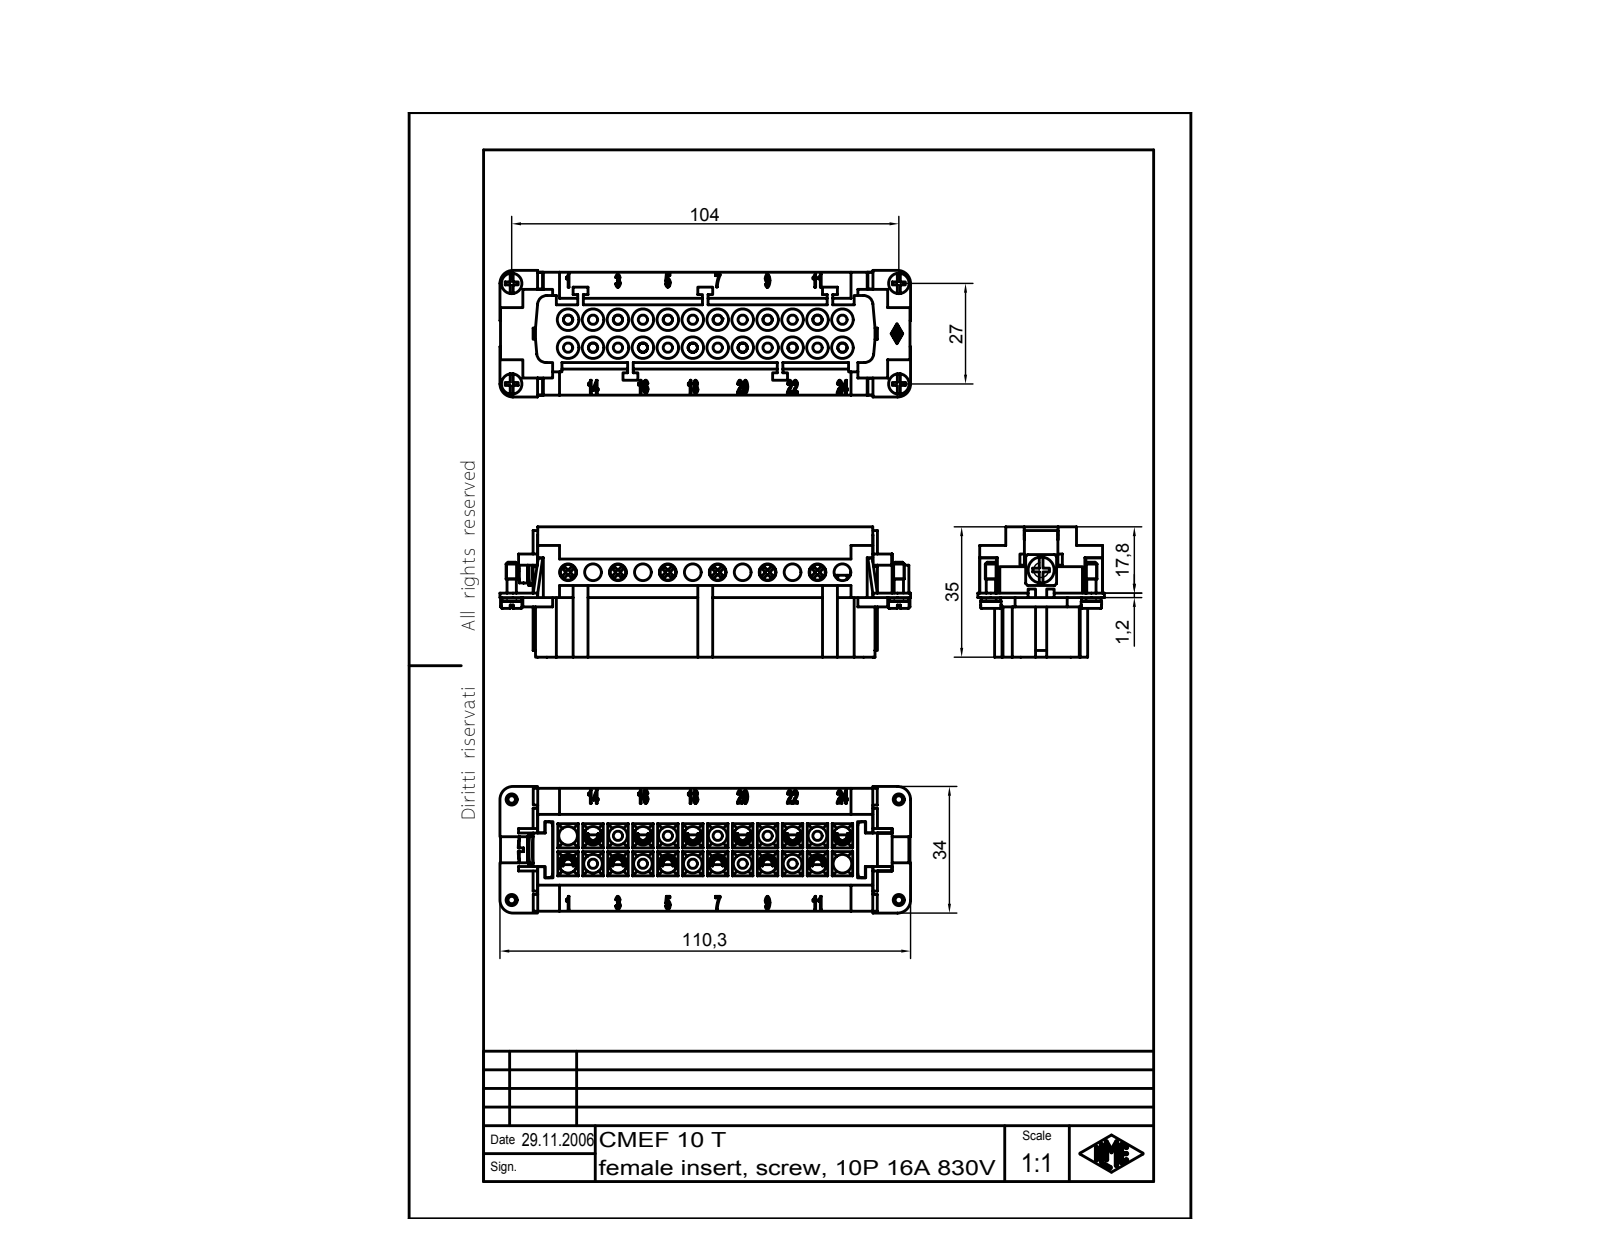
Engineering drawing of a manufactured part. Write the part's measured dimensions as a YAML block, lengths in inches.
part_name: "CMEF 10 T"
step_written_by: "Autodesk Inventor 7 (AUTOMOTIVE_DESIGN)"
units: inches
bodies: {solids: 25, faces: 1956, planar: 974, cylindrical: 286, other: 696}
overall_size: [4.343, 1.378, 1.339]
volume: 3.26
surface_area: 62.6
round_holes:
  - {diameter: 0.118, count: 12}
  - {diameter: 0.177, count: 12}
  - {diameter: 0.197, count: 11}
  - {diameter: 0.1, count: 2}
round_bosses_or_shafts:
  - {diameter: 0.098, count: 16}
  - {diameter: 0.165, count: 12}
  - {diameter: 0.217, count: 2}
  - {diameter: 0.209, count: 2}
  - {diameter: 0.197, count: 2}
  - {diameter: 0.118, count: 2}
  - {diameter: 0.276, count: 1}
partial_cylinders:
  - {radius: 0.004, count: 14}
  - {radius: 0.083, count: 12}
  - {radius: 0.098, count: 4}
  - {radius: 0.039, count: 2}
  - {radius: 0.138, count: 2}
  - {radius: 0.064, count: 1}
  - {radius: 0.217, count: 1}
face_to_face_distances: [0.069, 0.679, 0.748, 0.63, 0.61, 0.344, 0.276, 0.128, 0.28, 0.955]
hole_center_spacings: [0.528, 0.264, 1.055, 0.791, 1.583, 1.319, 0.396, 0.605]
